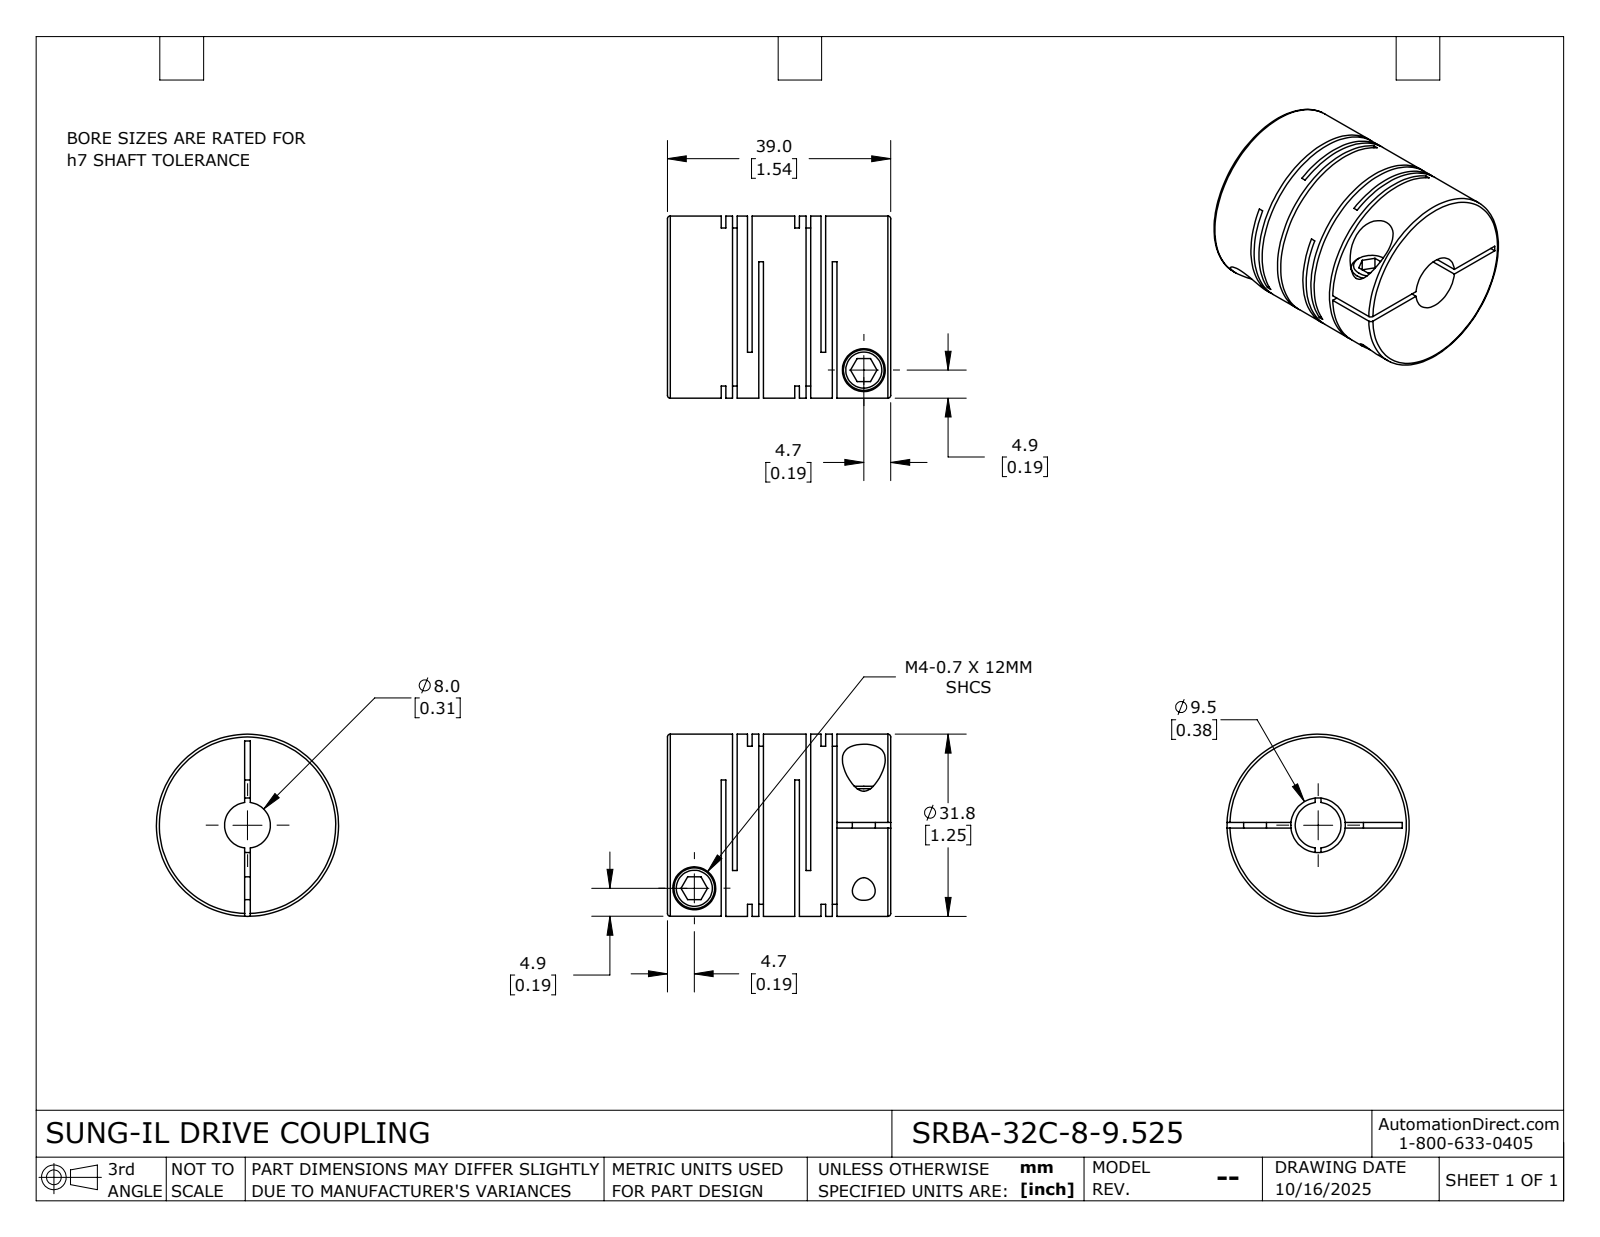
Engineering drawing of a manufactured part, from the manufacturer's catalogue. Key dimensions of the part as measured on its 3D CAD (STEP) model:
Part name (STEP PRODUCT): SRBA-32C-8-9.525
STEP written by: SolidWorks 2024 (CONFIG_CONTROL_DESIGN)
Units: millimetres
Bodies: 1 solid, 115 faces (60 planar, 42 cylindrical, 13 other)
Overall size (bounding box): 39 × 31.8 × 31.8
Volume: 23 841 mm³ · Surface area: 16 326 mm²
Round holes (diameter × count): ⌀4 ×2, ⌀7.5 ×2, ⌀8 ×1, ⌀9.53 ×1
Round bosses / shafts (diameter × count): ⌀7.1 ×2, ⌀31.8 ×1
Main face-to-face distances: 0.8, 12.84, 1.98, 4.58, 12.04, 1.18, 10.86, 3.78, 8.26, 2.6
